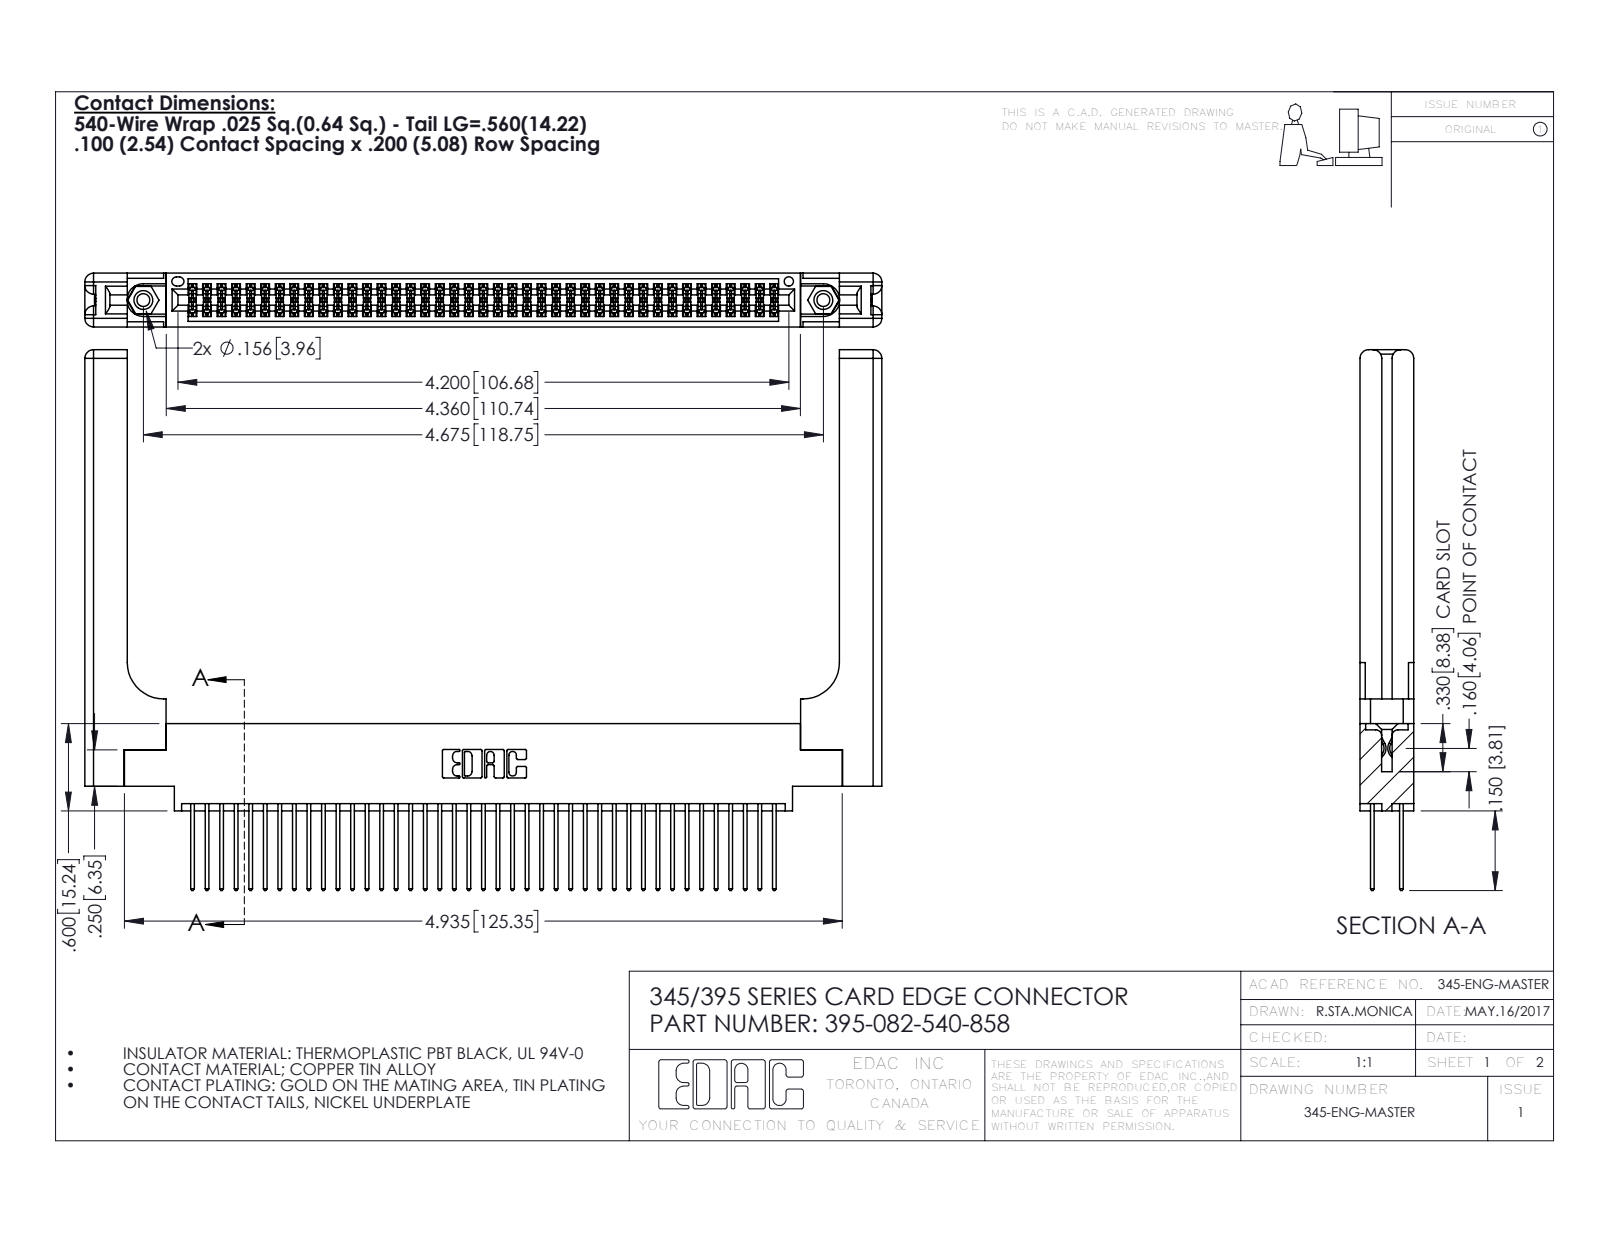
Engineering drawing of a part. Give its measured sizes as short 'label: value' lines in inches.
name: 345-220-058_345-220-058; 345 Part_0.170 Offset - 0.156 Dia-TH; 395-082-540-858; 345-292-001_345-293-140 (+1 more)
written by: SolidWorks 2016 (CONFIG_CONTROL_DESIGN)
unit: in
bodies: 87 solids, 4486 faces (2938 planar, 1488 cylindrical, 60 other)
size: 5.479 × 3.717 × 0.37
volume: 1.354 in³; area: 41.67 in²
holes: 2× ⌀0.089, 2× ⌀0.125, 2× ⌀0.156, 1× ⌀0.064
bosses: 2× ⌀0.155
rounds: 123× R0.006, 82× R0.01, 22× R0.01, 16× R0.06, 6× R0.007, 6× R0.031, 3× R0.026, 2× R0.014
face distances: 0.072, 0.298, 0.37, 0.098, 0.272, 0.025, 0.2, 0.225, 0.175, 0.148
hole spacings: 0.27, 4.439, 4.675
